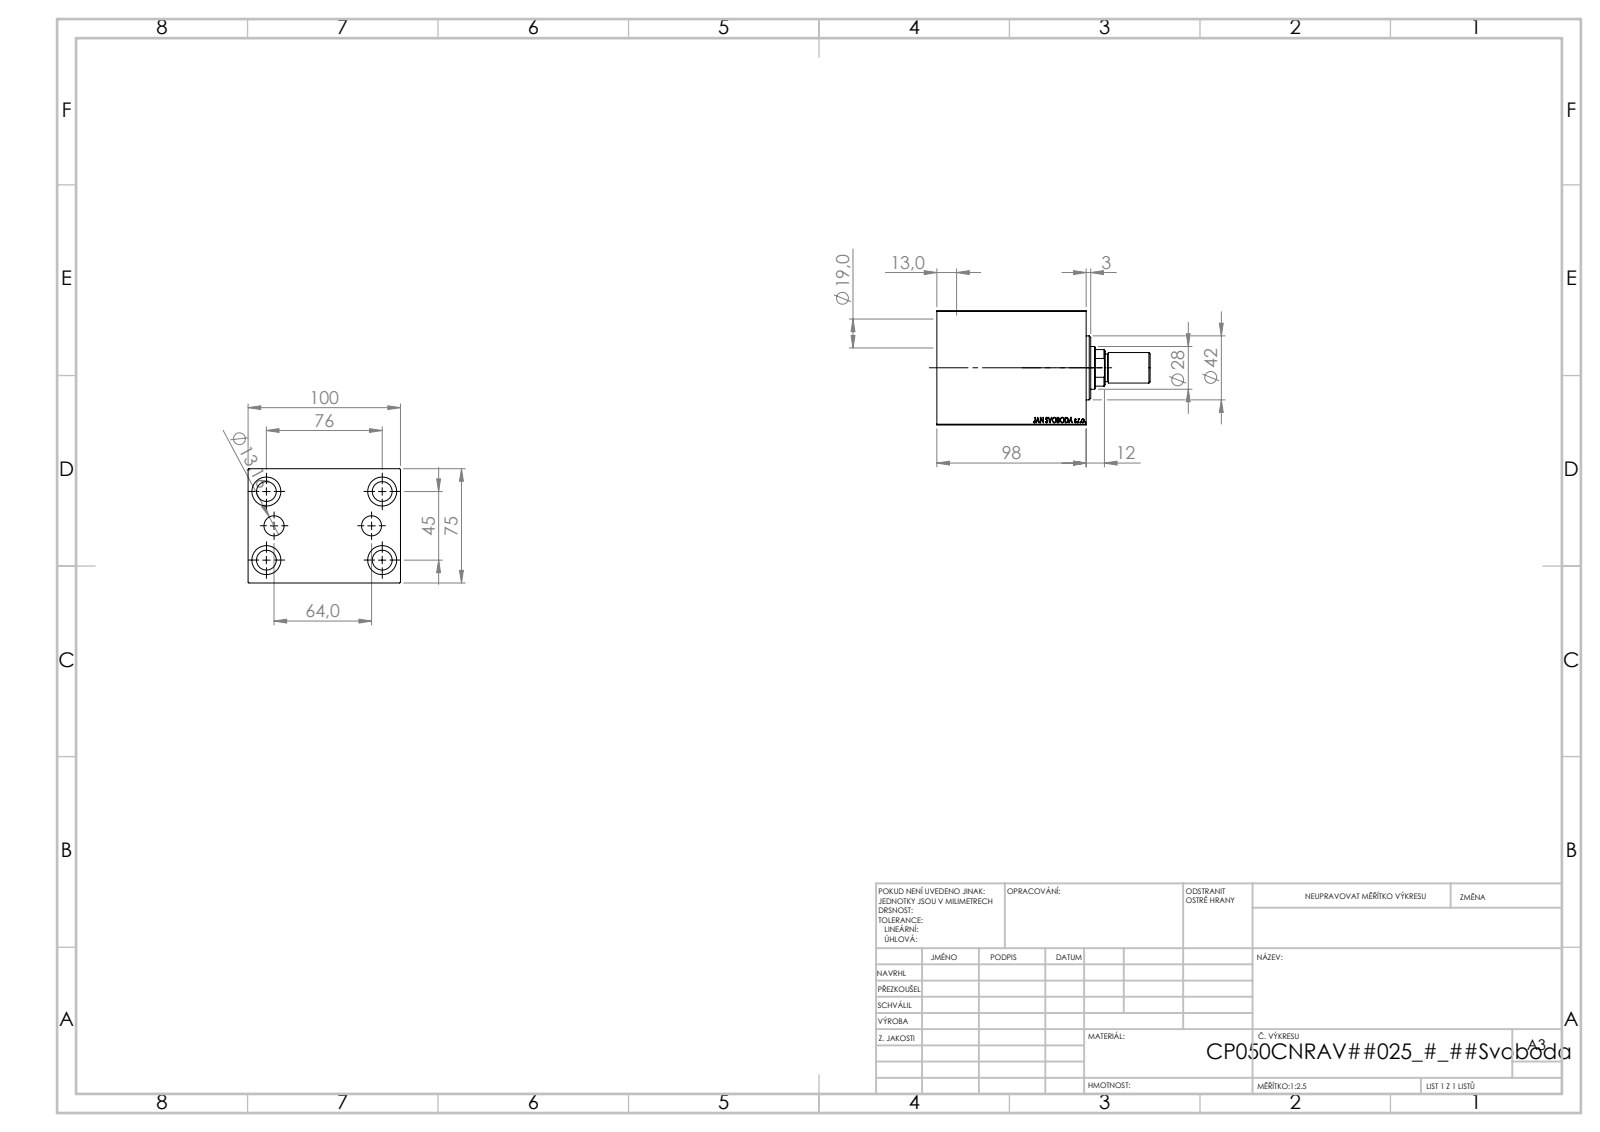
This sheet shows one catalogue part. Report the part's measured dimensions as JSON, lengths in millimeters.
{"part_name": "V450CM_C_VCP; V450CM_VC_B; V450CM_C_Body; V450CM_MALE_METRIC", "step_written_by": "SolidWorks 2019 (CONFIG_CONTROL_DESIGN)", "units": "millimeters", "bodies": {"solids": 4, "faces": 869, "planar": 411, "cylindrical": 58, "other": 400}, "overall_size": [140, 100, 75], "volume_mm3": 641636, "surface_area_mm2": 107688, "round_holes": [[13, 4], [19, 4], [13.16, 2], [18.5, 1], [28, 1], [31.5, 1], [50, 1], [52, 1], [57, 1]], "round_bosses_or_shafts": [[42, 1], [20, 1], [18, 1]], "partial_cylinders_radius": [[13.5, 1]], "face_to_face_distances": [75, 100, 98, 84, 14, 12, 72, 25, 86, 47], "hole_center_spacings": [44.16, 23.05, 23.56, 45, 72.58, 74.48, 76, 88.32]}
